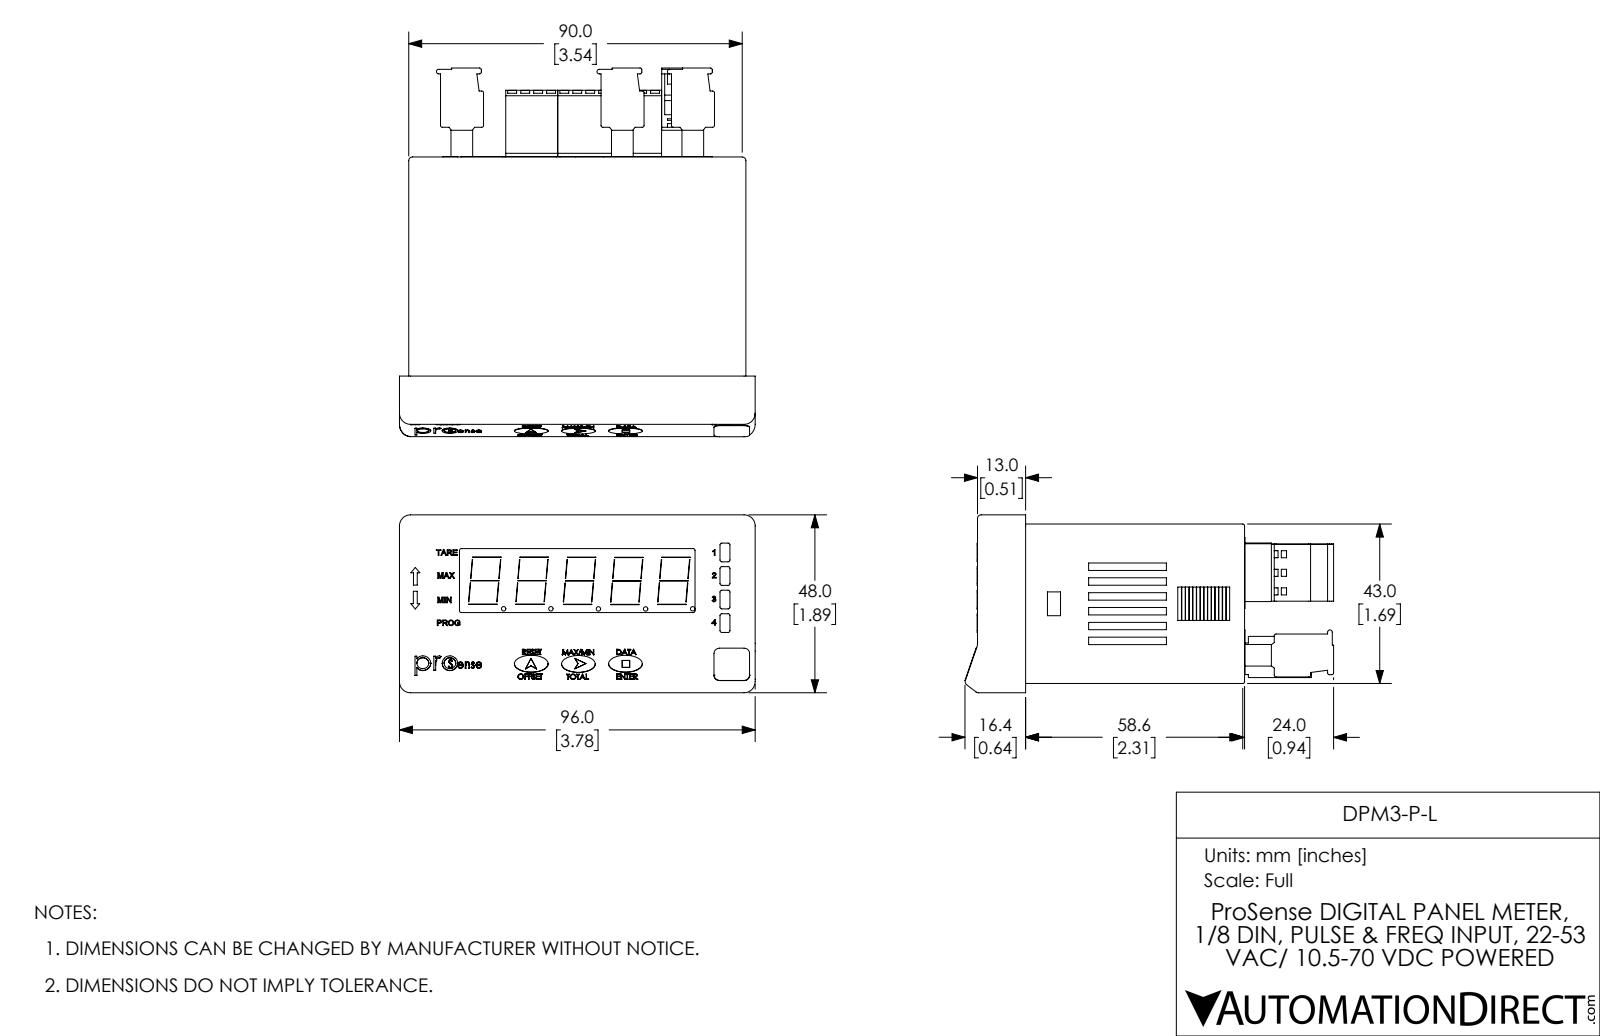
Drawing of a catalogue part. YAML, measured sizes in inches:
part_name: "DPM3-P Coord fXT"
step_written_by: "SolidWorks 2017 (AUTOMOTIVE_DESIGN)"
units: inches
bodies: {solids: 10, faces: 2760, planar: 2133, cylindrical: 368, other: 259}
overall_size: [3.916, 3.78, 1.89]
volume: 5.643
surface_area: 104.7
round_holes:
  - {diameter: 0.039, count: 12}
  - {diameter: 0.079, count: 12}
  - {diameter: 0.078, count: 10}
  - {diameter: 0.118, count: 10}
  - {diameter: 0.152, count: 10}
round_bosses_or_shafts:
  - {diameter: 0.047, count: 5}
partial_cylinders:
  - {radius: 0.004, count: 53}
  - {radius: 0.02, count: 42}
  - {radius: 0.012, count: 24}
  - {radius: 0.014, count: 24}
  - {radius: 0.07, count: 12}
  - {radius: 0.072, count: 12}
  - {radius: 0.118, count: 10}
  - {radius: 0.121, count: 10}
face_to_face_distances: [0.059, 1.634, 0.098, 1.693, 1.575, 1.732, 0.157, 3.524, 0.433, 2.78]
hole_center_spacings: [0.138, 0.276, 0.201, 0.197, 0.413, 0.748, 0.774, 0.197]
